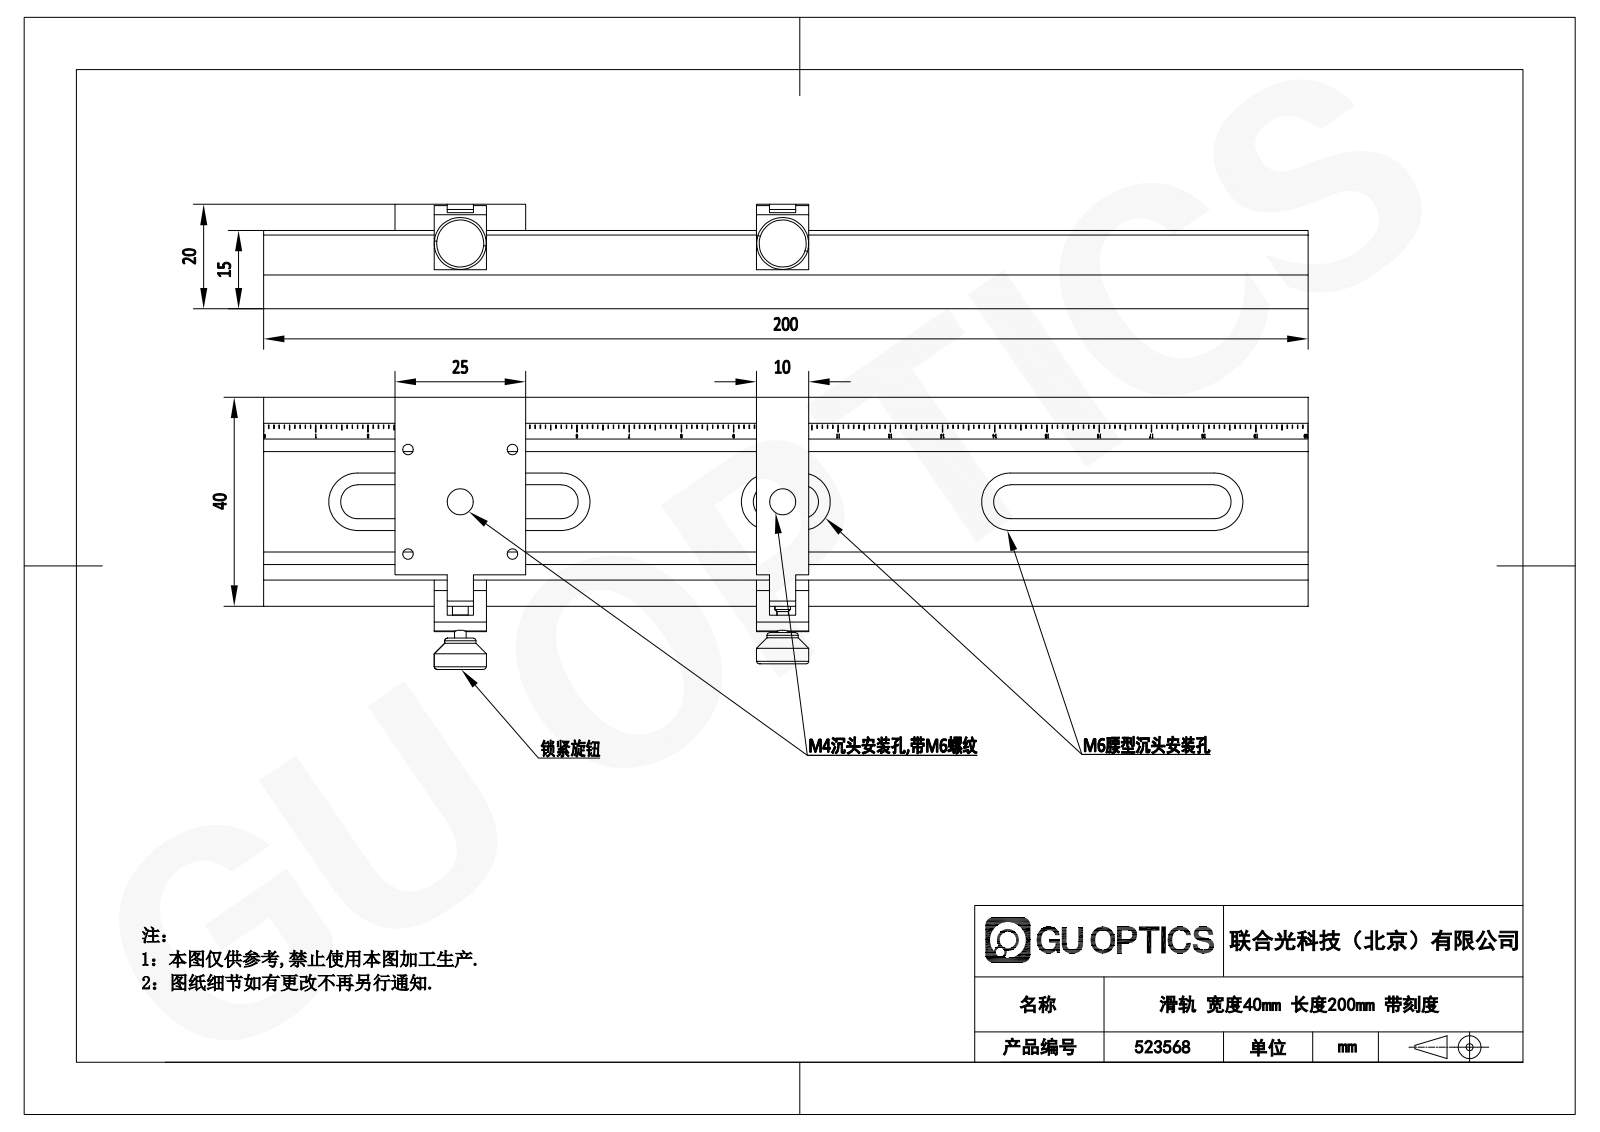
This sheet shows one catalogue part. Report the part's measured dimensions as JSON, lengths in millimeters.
{"part_name": "523568", "step_written_by": "SolidWorks 2020 (CONFIG_CONTROL_DESIGN)", "units": "millimeters", "bodies": {"solids": 8, "faces": 1835, "planar": 1444, "cylindrical": 83, "other": 308}, "overall_size": [200, 52.09, 20], "volume_mm3": 78110, "surface_area_mm2": 34068, "round_holes": [[2.05, 4], [2.5, 2], [3.2, 2], [5, 2], [8, 2], [1.5, 1], [2, 1]], "round_bosses_or_shafts": [[10, 2], [6, 2], [3, 2], [2.2, 2]], "partial_cylinders_radius": [[3.25, 6], [5.5, 6], [1.25, 1], [2.5, 1], [4.5, 1], [12.5, 1]], "face_to_face_distances": [14.5, 6, 0.5, 15, 5, 6.5, 8.5, 8, 40, 19.5], "hole_center_spacings": [14.14, 20, 28.28, 52.66, 61.7, 72.39]}
